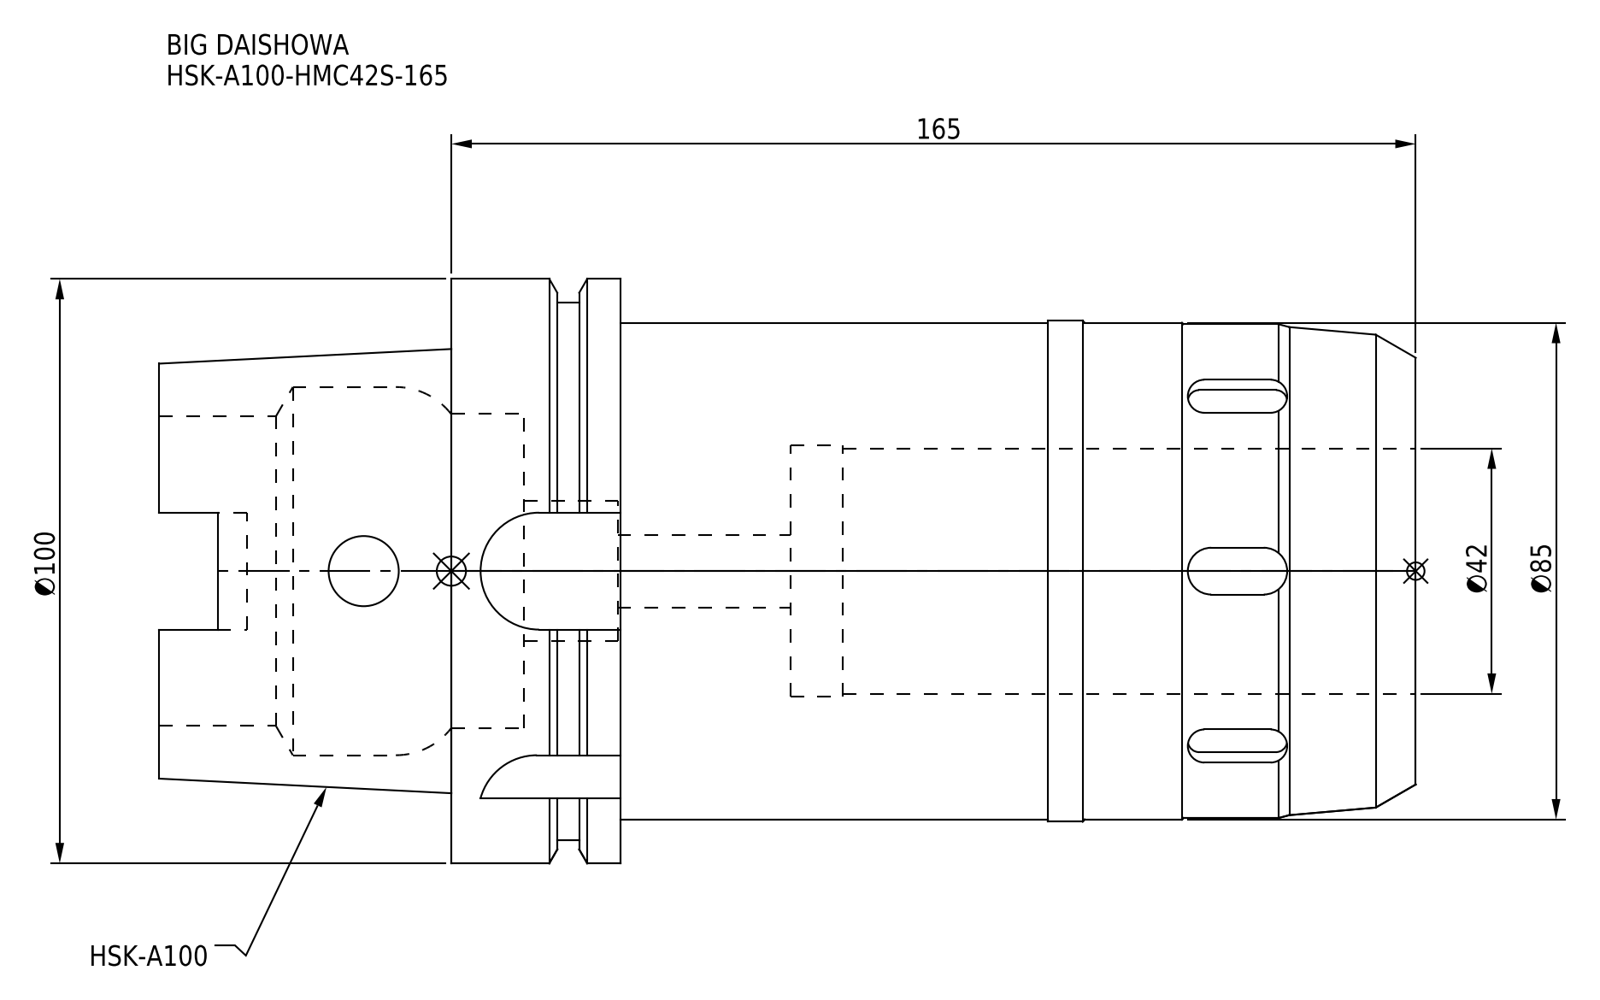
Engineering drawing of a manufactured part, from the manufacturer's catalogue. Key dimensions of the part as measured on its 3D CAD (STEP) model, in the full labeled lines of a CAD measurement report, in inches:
Part name (STEP PRODUCT): HSK-A100-HMC42S-165
STEP written by: CREO PARAMETRIC BY PTC INC, 2016380 (AUTOMOTIVE_DESIGN)
Units: inches
Bodies: 1 solid, 147 faces (59 planar, 60 cylindrical, 28 other)
Overall size (bounding box): 8.465 × 3.937 × 3.937
Volume: 52.37 in³ · Surface area: 156.2 in²
Round holes (diameter × count): ⌀0.472 ×1, ⌀0.488 ×1, ⌀0.945 ×1, ⌀1.654 ×1, ⌀1.693 ×1, ⌀2.087 ×1, ⌀2.118 ×1, ⌀2.48 ×1
Round bosses / shafts (diameter × count): ⌀3.937 ×1, ⌀3.622 ×1, ⌀3.374 ×1, ⌀3.346 ×1, ⌀3.327 ×1
Partial cylindrical surfaces — rounded edges, fillets, slot ends (radius × count): R0.157 ×12, R0.192 ×4, R0.394 ×4
Main face-to-face distances: 1.142, 6.496, 5.354, 6.006, 0.652, 0.49, 1.969, 4.213, 8.465, 3.11
